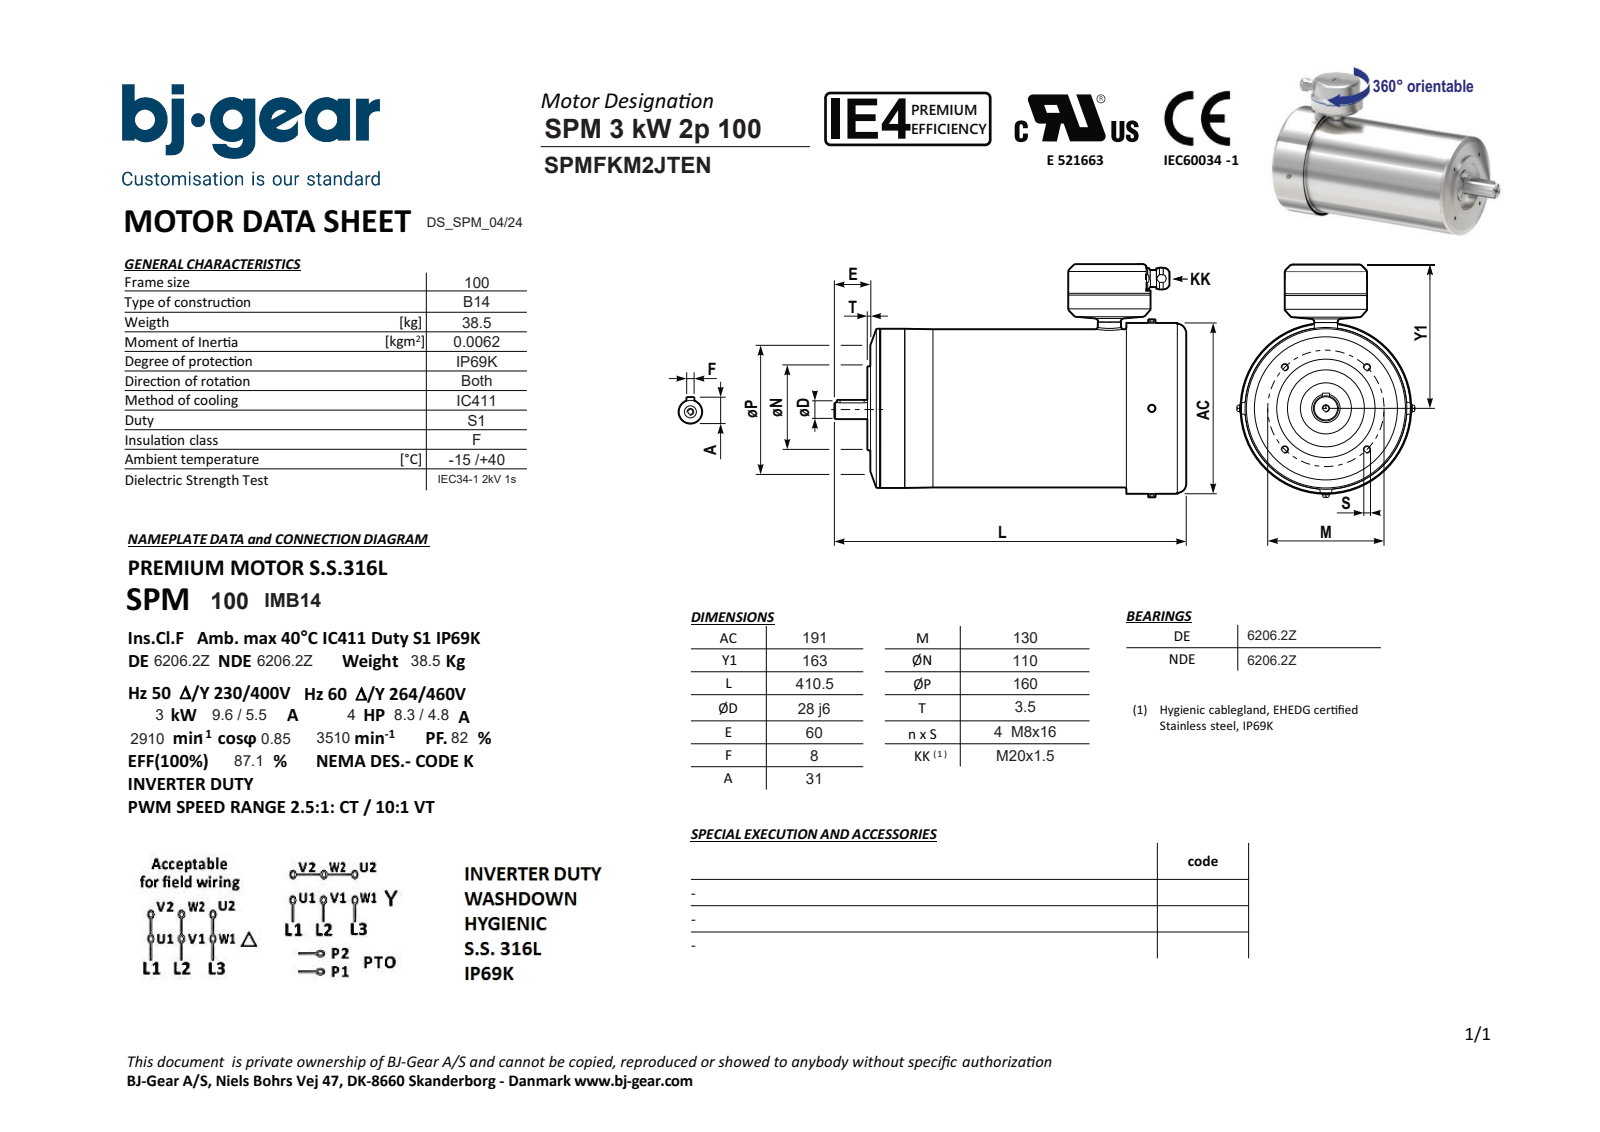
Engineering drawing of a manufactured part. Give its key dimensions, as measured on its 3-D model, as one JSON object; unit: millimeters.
{"part_name": "SPMFKM2JTEVN4KFU1-N---NNN", "step_written_by": "Solid Edge (AUTOMOTIVE_DESIGN)", "units": "millimeters", "bodies": {"solids": 1, "faces": 210, "planar": 81, "cylindrical": 65, "other": 64}, "overall_size": [410.5, 261.5, 199], "volume_mm3": 9353000, "surface_area_mm2": 293797, "round_holes": [[6.65, 4], [4.92, 1], [7, 1], [8.4, 1], [13.4, 1], [16, 1], [85, 1]], "round_bosses_or_shafts": [[9, 2], [191, 1], [178, 1], [177.98, 1], [110, 1], [93, 1], [84, 1], [30, 1]], "partial_cylinders_radius": [[4, 4], [12.8, 1]], "face_to_face_distances": [350.5, 6, 344.5, 67, 277.5, 283.5, 3, 353.5, 286.5, 9], "hole_center_spacings": [65, 91.92, 110.55, 129.99, 197.87, 146.5]}
